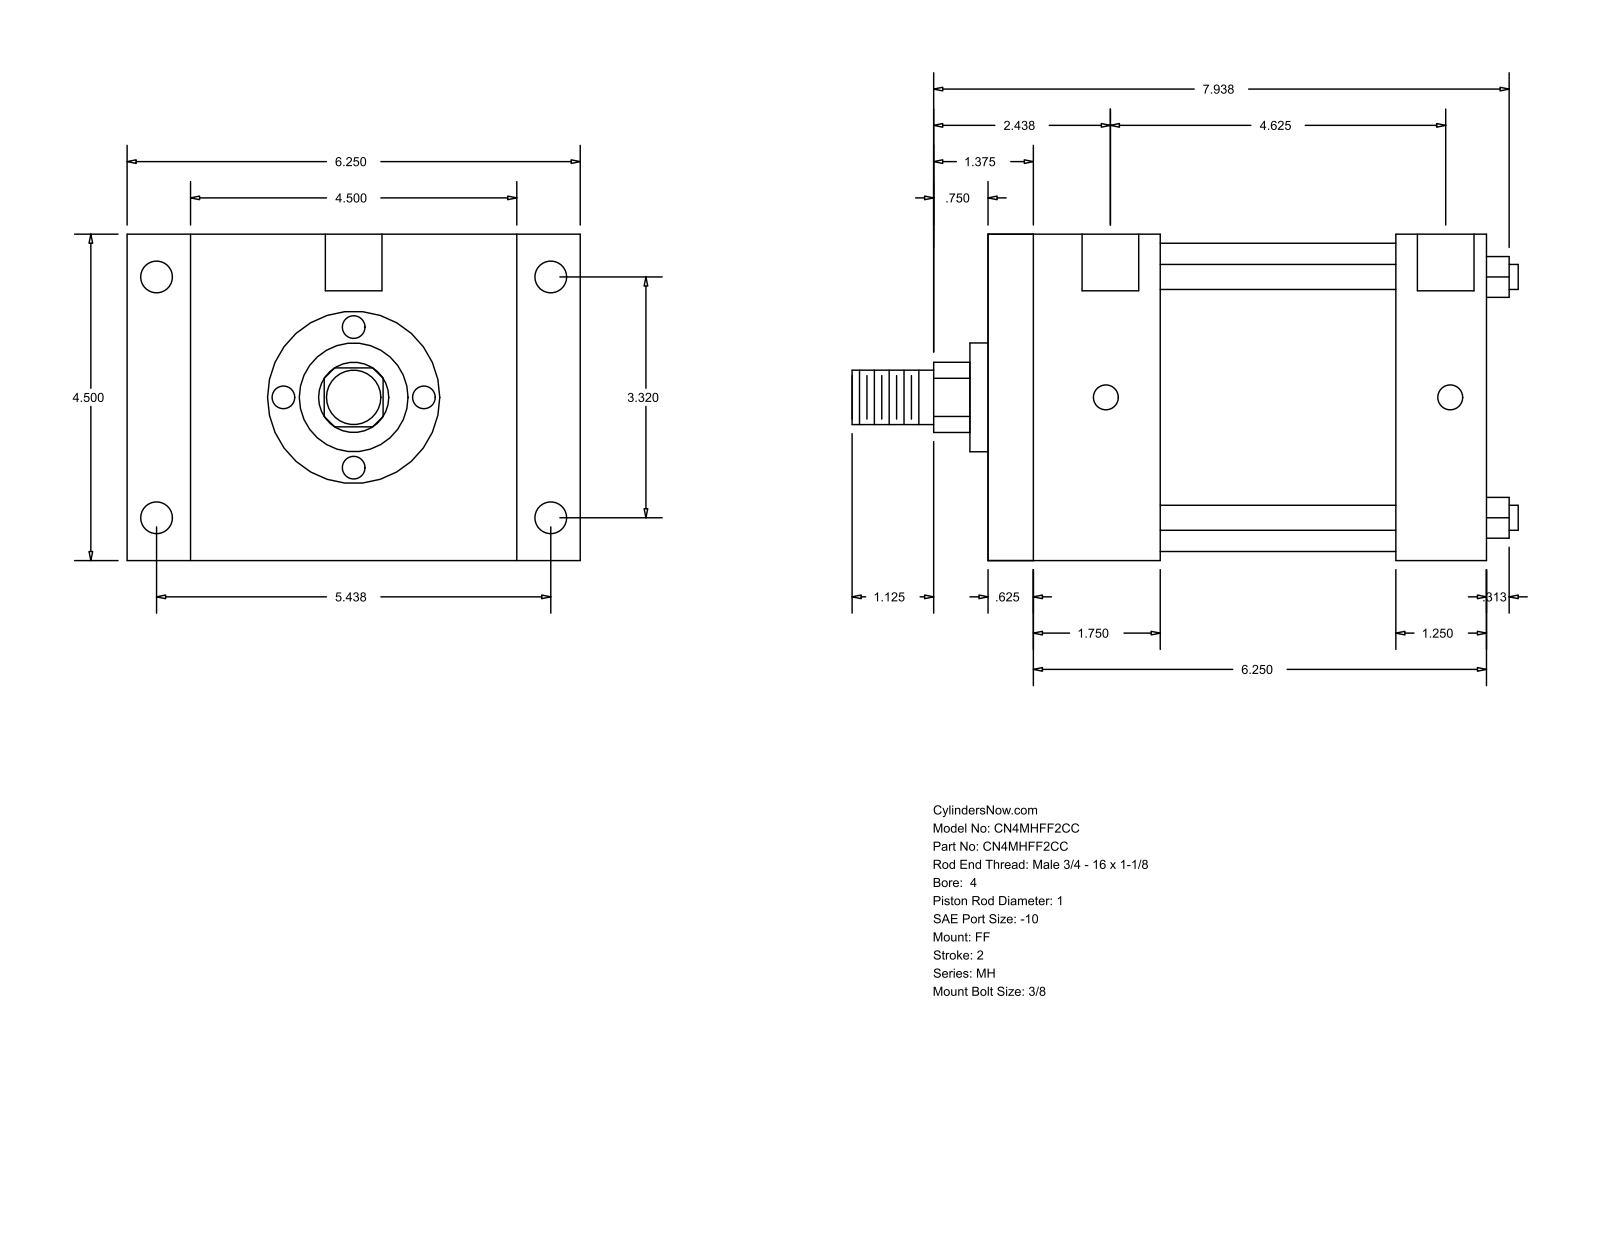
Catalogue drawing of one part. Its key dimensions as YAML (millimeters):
part_name: "MH_FF__0400_1"
step_written_by: "GSSL Pune (CONFIG_CONTROL_DESIGN)"
units: millimeters
bodies: {solids: 0, faces: 92, planar: 64, cylindrical: 28, other: 0}
overall_size: [233.36, 158.75, 114.3]
round_holes:
  - {diameter: 8.73, count: 4}
  - {diameter: 11.13, count: 4}
  - {diameter: 19.84, count: 2}
round_bosses_or_shafts:
  - {diameter: 8.76, count: 4}
  - {diameter: 107.95, count: 1}
  - {diameter: 38.1, count: 1}
  - {diameter: 25.4, count: 1}
  - {diameter: 19.05, count: 1}
partial_cylinders:
  - {radius: 12.29, count: 1}
face_to_face_distances: [114.3, 174.63, 158.76, 15.87, 60.33, 44.46, 142.88, 127.01, 82.55, 31.75]
hole_center_spacings: [1.58, 84.32, 119.06, 120.64, 138.12, 161.82, 117.48]
